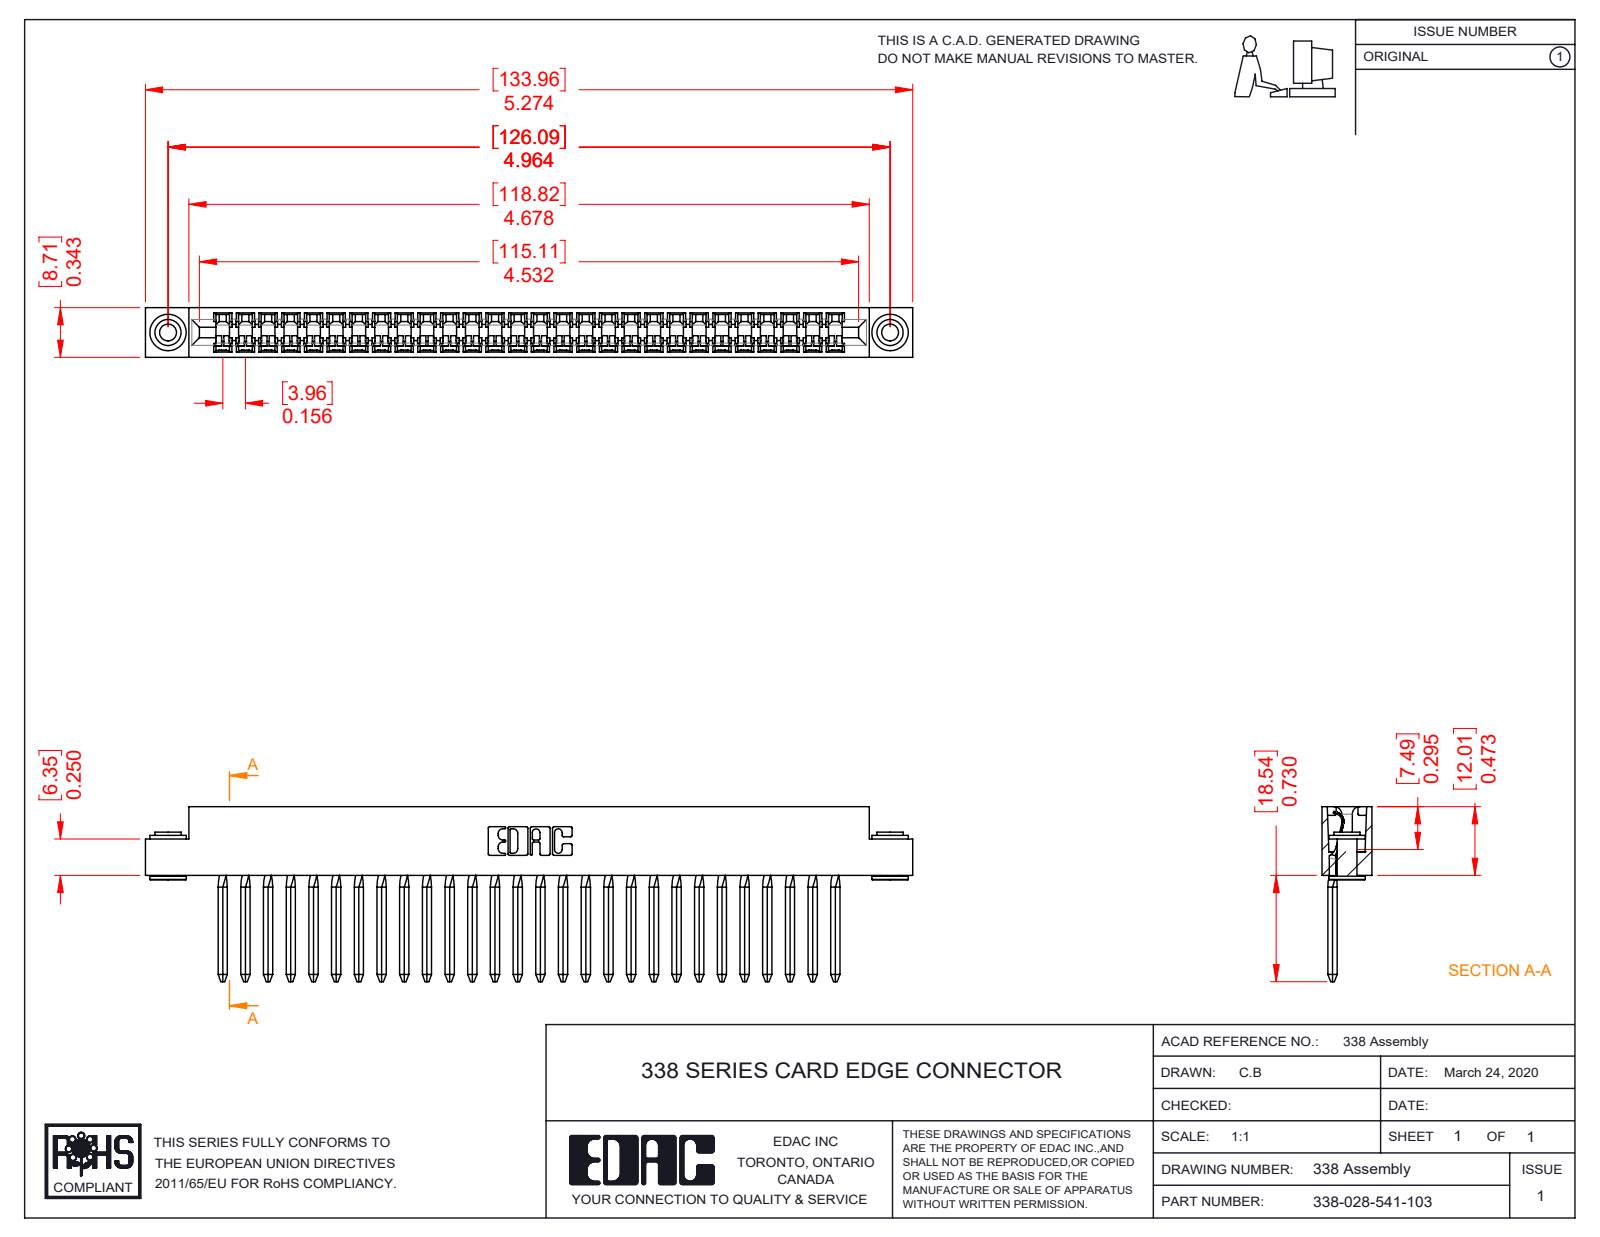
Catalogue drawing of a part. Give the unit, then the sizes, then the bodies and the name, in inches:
Units: inches
Overall size (bounding box): 5.274 × 1.203 × 0.343
Round holes (diameter × count): ⌀0.116 ×2, ⌀0.156 ×2
Round bosses / shafts (diameter × count): ⌀0.25 ×2, ⌀0.18 ×2, ⌀0.136 ×2
Partial cylindrical surfaces — rounded edges, fillets, slot ends (radius × count): R0.025 ×114, R0.008 ×28, R0.055 ×23, R0.067 ×23, R0.01 ×22, R0.1 ×22, R0.007 ×6, R0.031 ×6
Main face-to-face distances: 0.343, 0.156, 0.11, 0.207, 0.135, 0.624, 0.78, 0.468, 0.048, 0.16
Hole centre spacings: 4.964
Volume: 0.574 in³ · Surface area: 24.26 in²
Bodies: 31 solids, 2750 faces (1894 planar, 736 cylindrical, 120 other)
Part name (STEP PRODUCT): 338-290-001_541; 338-210-001_338-210-028-004; 338-028-541-103; 345-250-002_345-250-002-102
STEP written by: SolidWorks 2016 (CONFIG_CONTROL_DESIGN)
